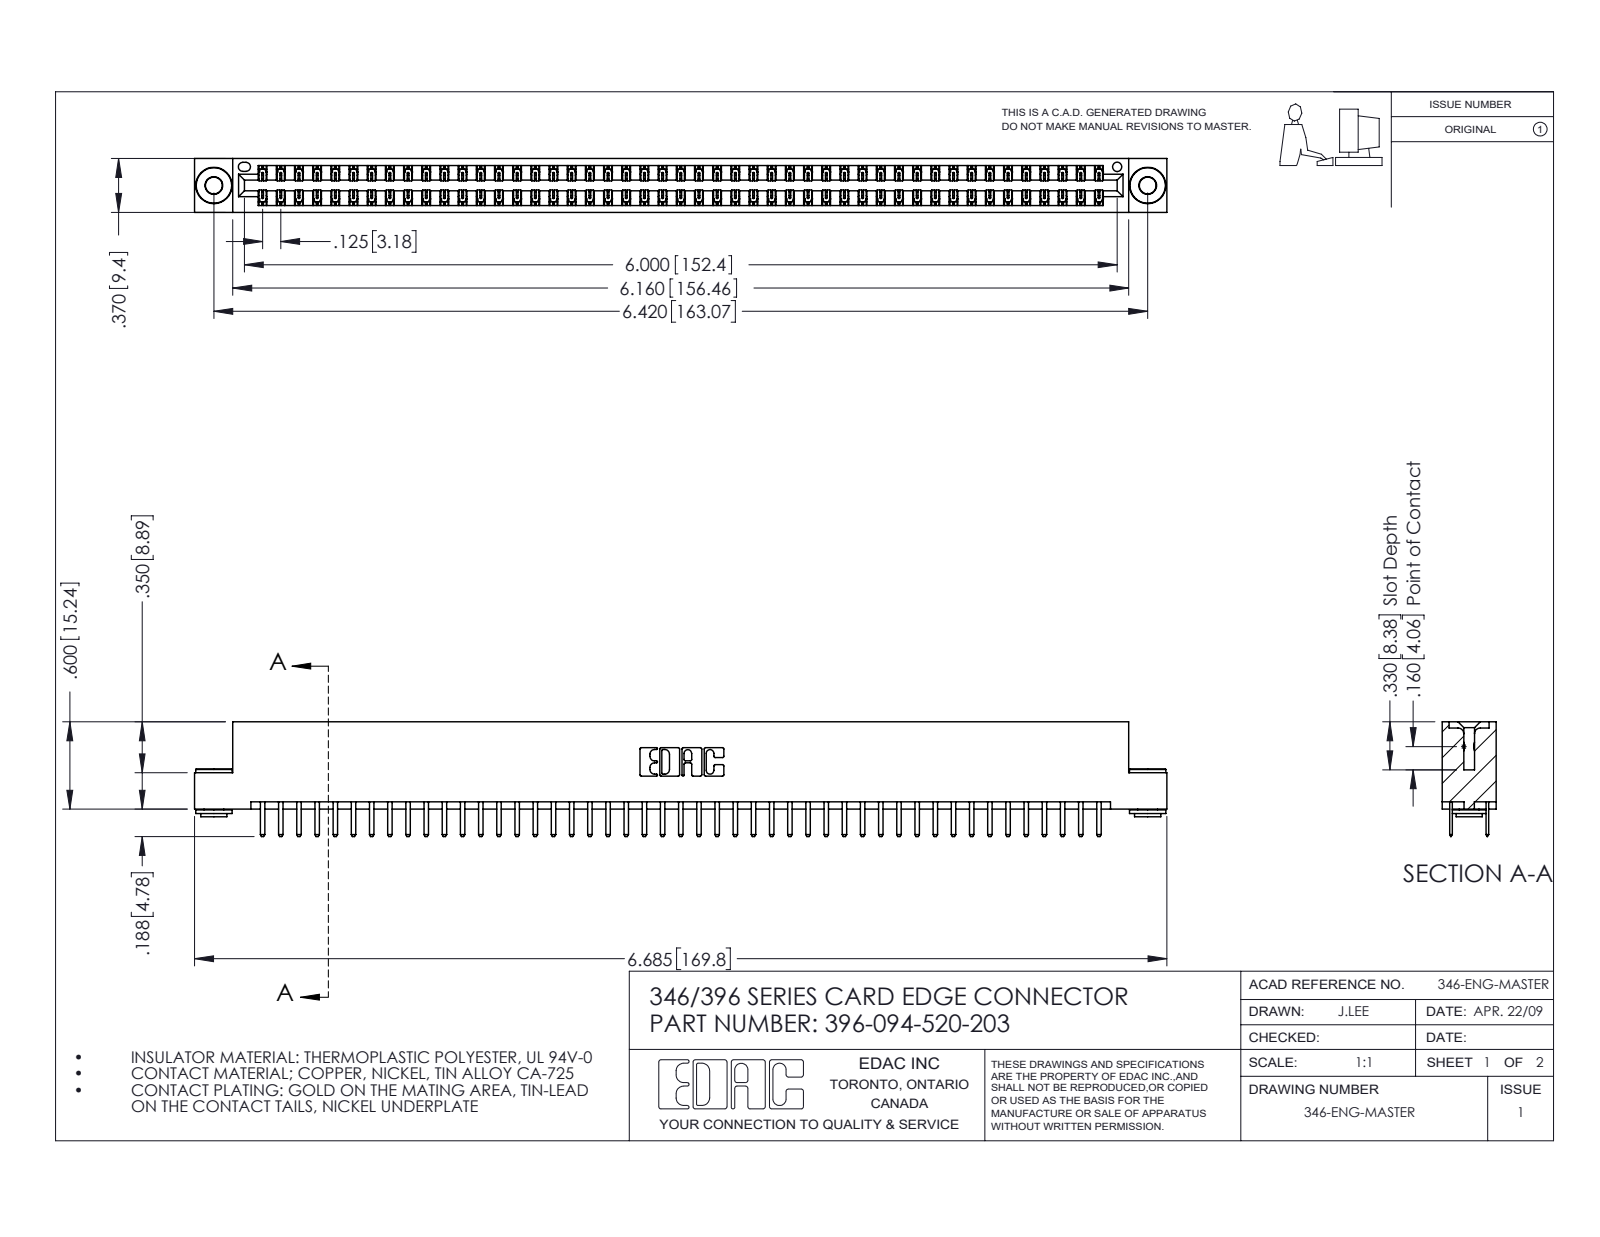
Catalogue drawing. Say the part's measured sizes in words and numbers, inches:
The part is named "396-094-520-203; 345-250-002_345-250-002-102; 345-292-001_345-293-120; 346 Part_Flush Mounting Lugs - 0.156 Dia-TH". Its 3-D file was written by "SolidWorks 2016 (CONFIG_CONTROL_DESIGN)". It is 97 solids with 5424 faces: 3564 planar, 1852 cylindrical and 8 other. Overall it measures 6.685 by 0.788 by 0.37 inches. Its volume is 1.011 cubic inches and its surface area 35.62 square inches. Round holes: 2 of diameter 0.116, 2 of diameter 0.156, 1 of diameter 0.064. Round bosses or shafts: 2 of diameter 0.25, 2 of diameter 0.18, 2 of diameter 0.136. Partial cylindrical surfaces (rounded edges, fillets, slot ends): 141 of radius 0.006, 98 of radius 0.01, 22 of radius 0.01, 6 of radius 0.007, 6 of radius 0.031, 3 of radius 0.026, 2 of radius 0.014, 2 of radius 0.022. The main face-to-face distances are 0.048, 0.322, 0.25, 0.37, 0.025, 0.275, 0.072, 0.298, 0.148, 0.222. The hole center spacings are 0.246, 6.211, 6.42.
